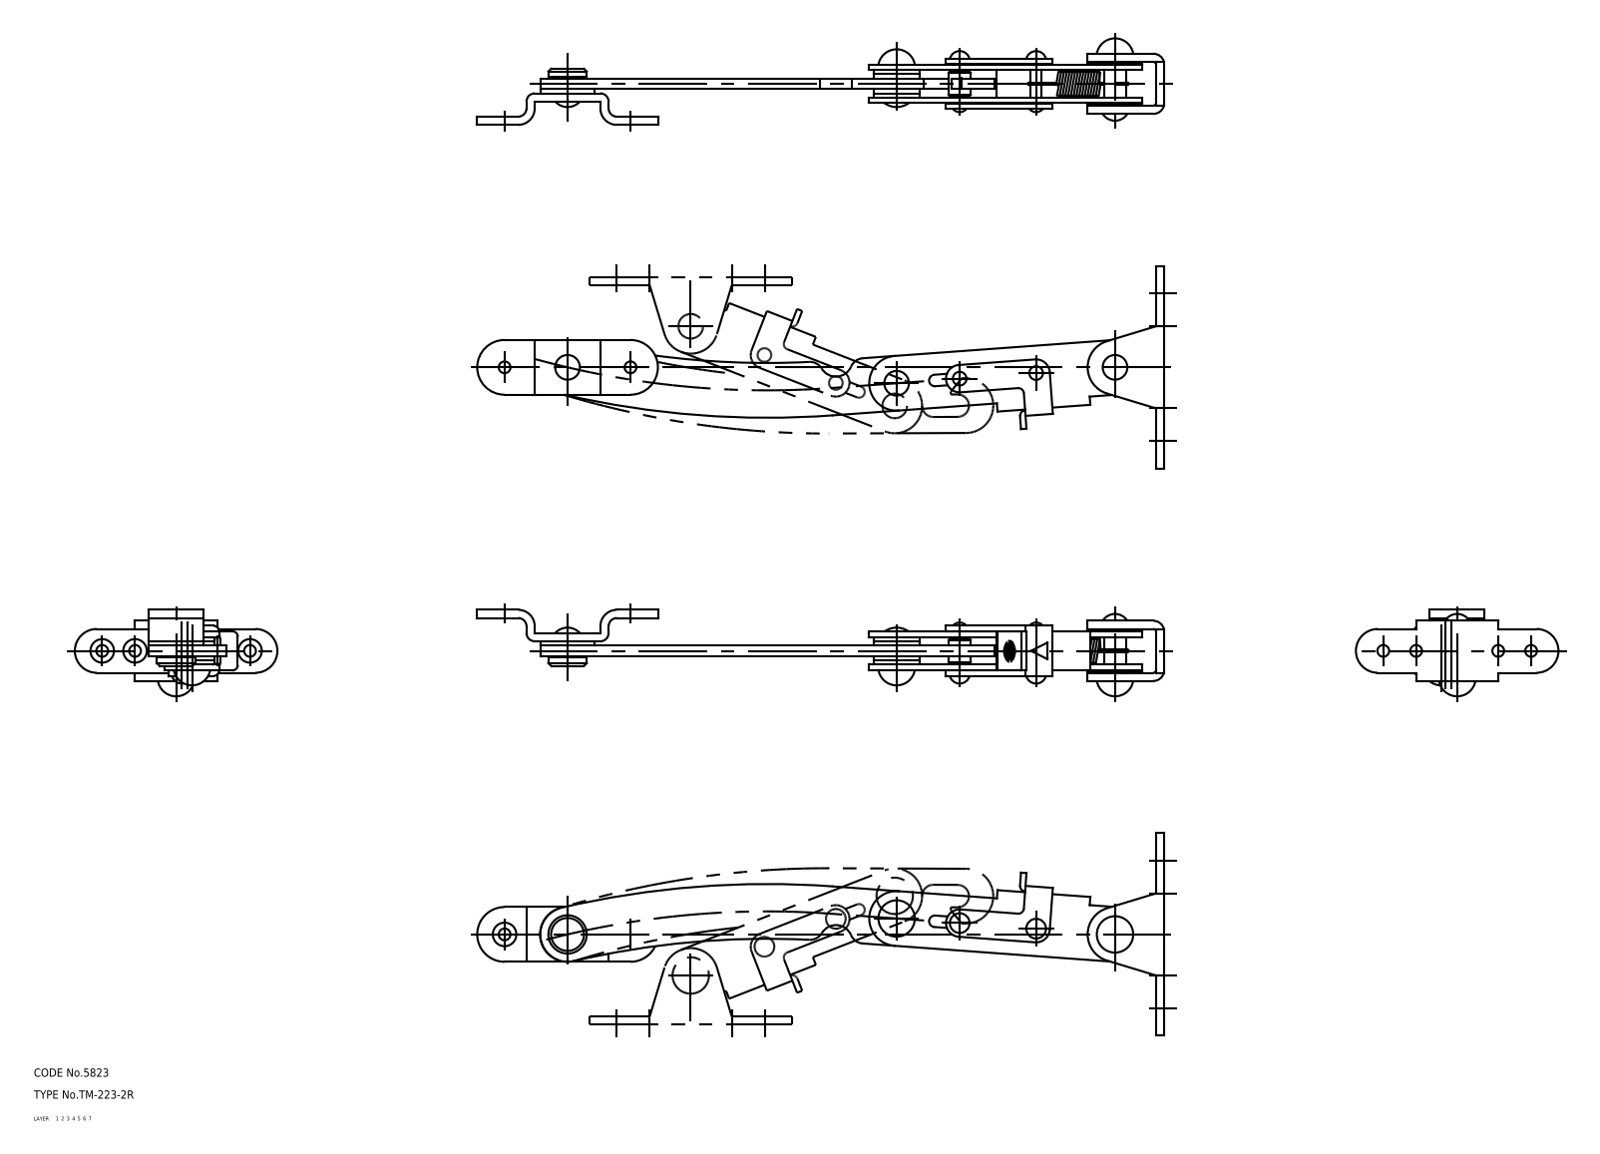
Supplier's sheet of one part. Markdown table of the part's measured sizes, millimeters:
| quantity | value |
| --- | --- |
| part name | spring_mr; spacer_C_mr-1; washer_mr-3; washer_mr-2 (+8 more) |
| STEP written by | CADfix (AUTOMOTIVE_DESIGN) |
| units | millimeters |
| bodies | 19 solids, 287 faces (0 planar, 0 cylindrical, 287 other) |
| overall size | 251 × 74 × 31.6 |
| volume | 38 773 mm³ |
| surface area | 35 888 mm² |
